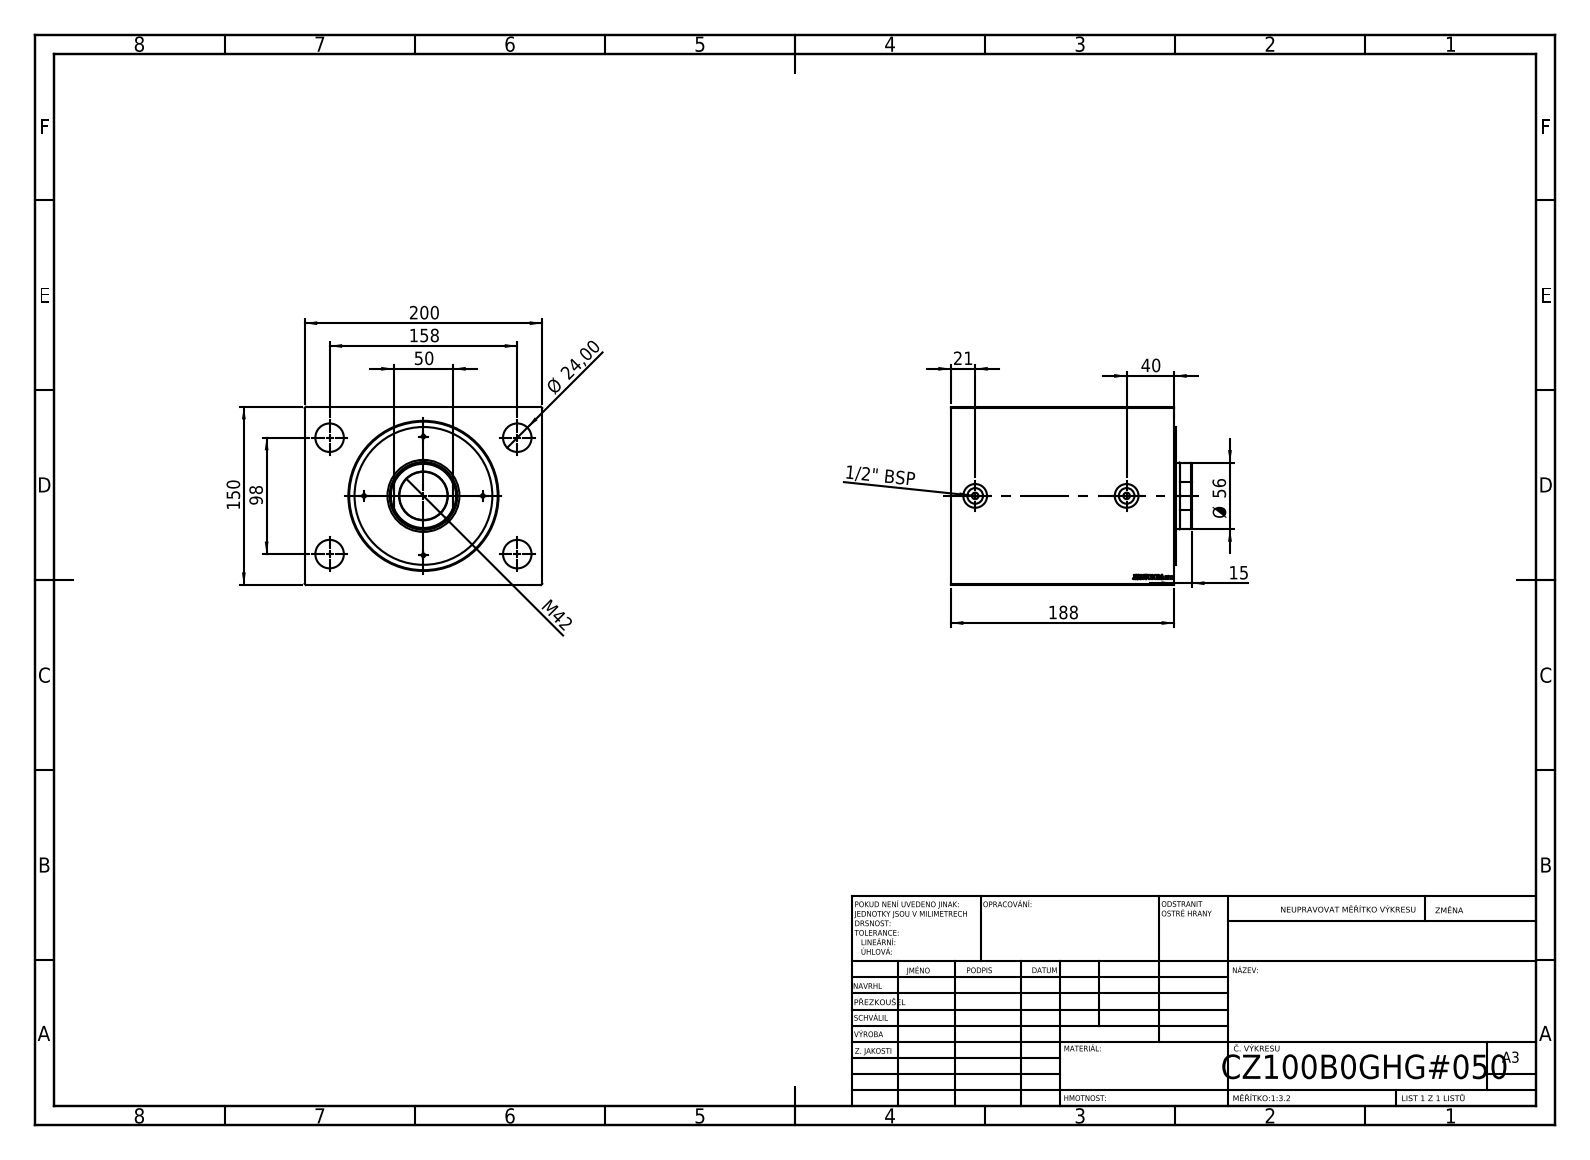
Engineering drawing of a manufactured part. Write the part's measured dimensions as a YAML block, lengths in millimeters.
part_name: "V500CZ_B_VC; V500CZ"
step_written_by: "SolidWorks 2019 (CONFIG_CONTROL_DESIGN)"
units: millimeters
bodies: {solids: 3, faces: 874, planar: 400, cylindrical: 58, other: 416}
overall_size: [203, 200, 150]
volume: 5211000
surface_area: 351594
round_holes:
  - {diameter: 3, count: 4}
  - {diameter: 24, count: 4}
  - {diameter: 5.5, count: 2}
  - {diameter: 13.16, count: 2}
  - {diameter: 20, count: 2}
  - {diameter: 36, count: 1}
  - {diameter: 40.5, count: 1}
  - {diameter: 56, count: 1}
  - {diameter: 57, count: 1}
  - {diameter: 100, count: 1}
  - {diameter: 125, count: 1}
round_bosses_or_shafts:
  - {diameter: 116, count: 1}
partial_cylinders:
  - {radius: 27.5, count: 1}
face_to_face_distances: [150, 200, 188, 154.7, 33.3, 15, 1.8, 13.2, 141.5, 174.8]
hole_center_spacings: [50, 56.94, 70.71, 79.01, 92.96, 126.66, 137.99, 98]
